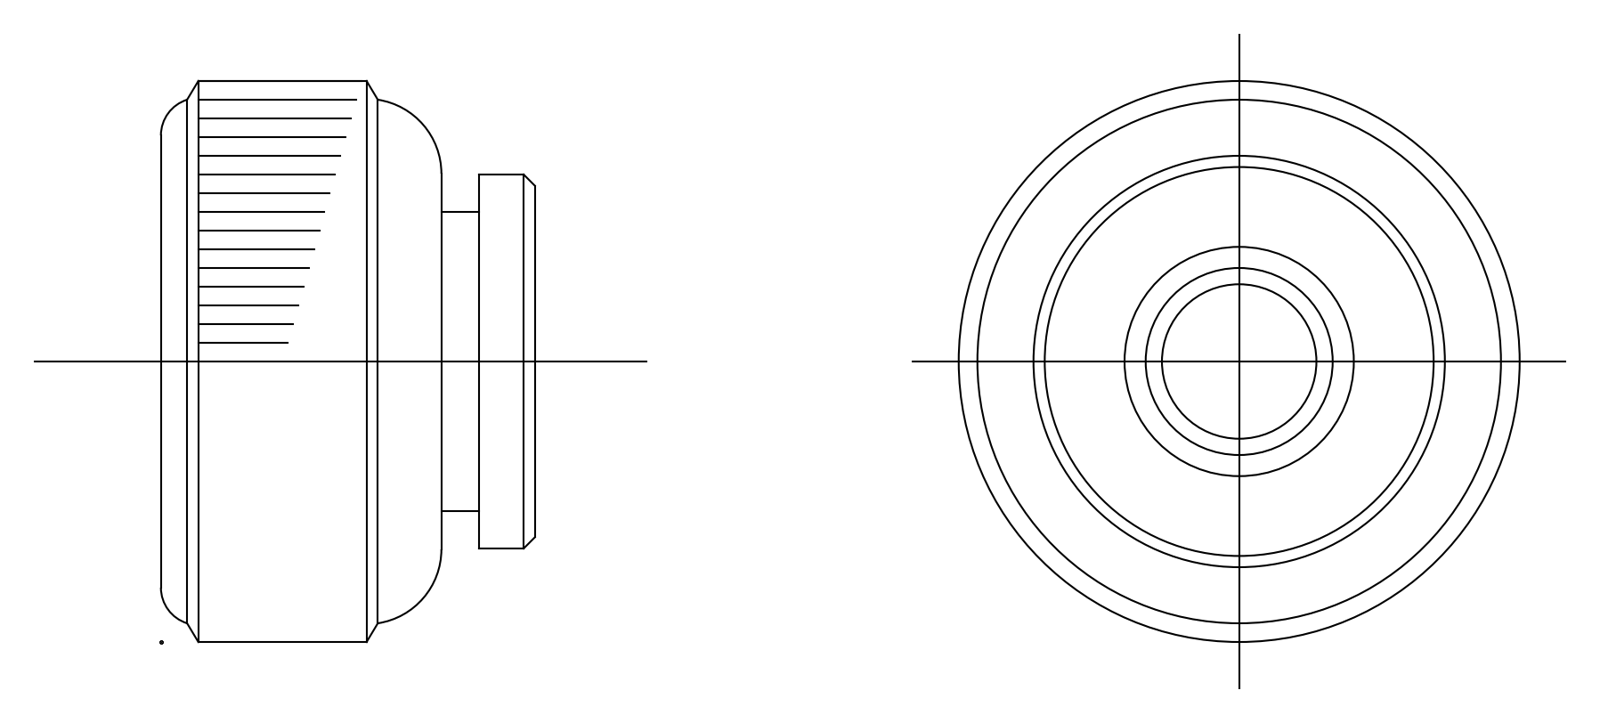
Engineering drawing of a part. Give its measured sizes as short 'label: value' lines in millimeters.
written by: spGate 20.6.3 (****-****-****-****) (AUTOMOTIVE_DESIGN)
unit: mm
bodies: 1 solid, 30 faces (4 planar, 10 cylindrical, 16 other)
size: 15 × 15 × 10
volume: 1 251 mm³; area: 847 mm²
holes: 1× ⌀3.65, 1× ⌀5
bosses: 1× ⌀15, 1× ⌀10, 1× ⌀8
face distances: 10, 7.5, 2.5, 8.5, 1, 1.5
